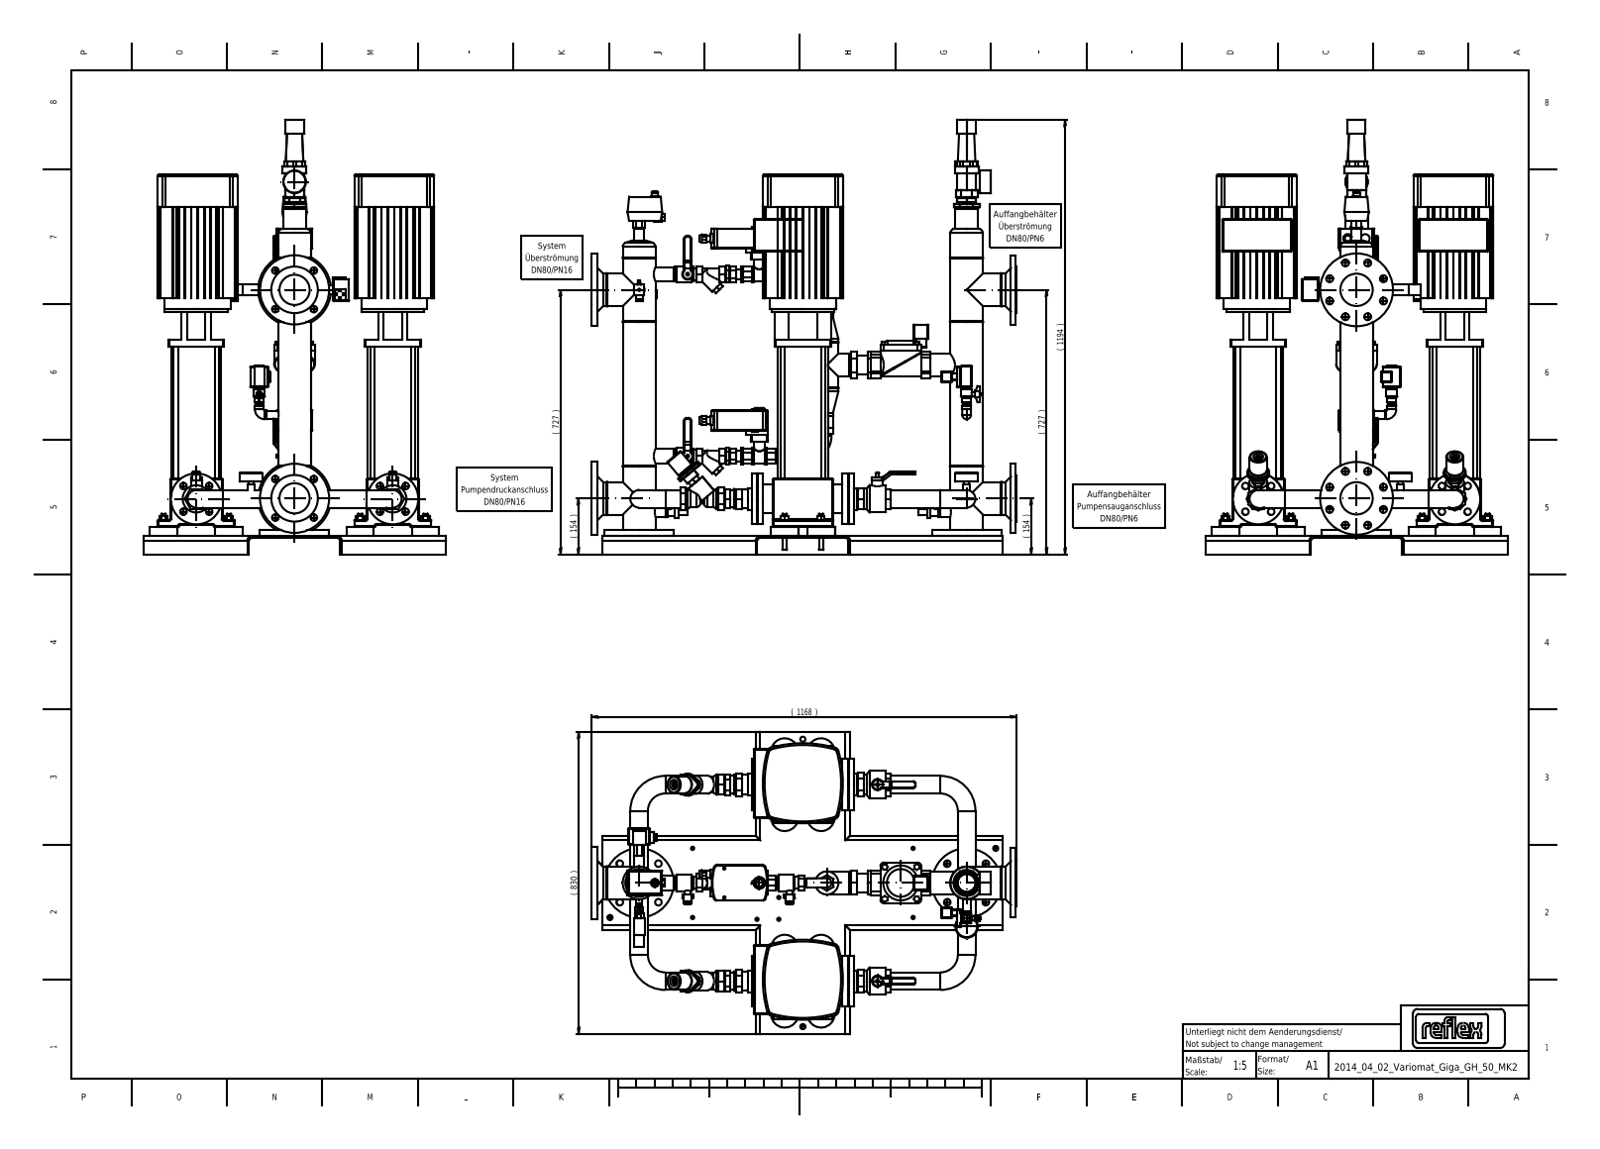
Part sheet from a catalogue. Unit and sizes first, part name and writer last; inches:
Units: inches
Overall size (bounding box): 47.024 × 45.984 × 32.677
Round holes (diameter × count): ⌀0.709 ×25, ⌀0.748 ×16, ⌀0.551 ×11, ⌀0.354 ×8, ⌀0.256 ×2, ⌀1.575 ×2, ⌀3.268 ×2, ⌀3.5 ×2
Round bosses / shafts (diameter × count): ⌀0.472 ×17, ⌀2.953 ×10, ⌀0.315 ×6, ⌀1.181 ×5, ⌀0.709 ×5, ⌀3.543 ×4, ⌀1.902 ×4, ⌀1.772 ×4
Partial cylindrical surfaces — rounded edges, fillets, slot ends (radius × count): R0.079 ×83, R0.098 ×70, R0.039 ×48, R0.118 ×8, R0.472 ×8, R12.795 ×8, R0.177 ×6, R0.394 ×5
Main face-to-face distances: 0.197, 0.669, 24.803, 24.606, 14.567, 21.26, 0.63, 0.079, 0.551, 10.039
Hole centre spacings: 3.15, 1.206, 3.394, 4.176, 4.454, 5.075, 5.985, 22.559
Volume: 4 784 in³ · Surface area: 9 781 in²
Bodies: 67 solids, 3432 faces (1290 planar, 948 cylindrical, 1194 other)
STEP written by: Mechanical Desktop 2011 (CONFIG_CONTROL_DESIGN)
